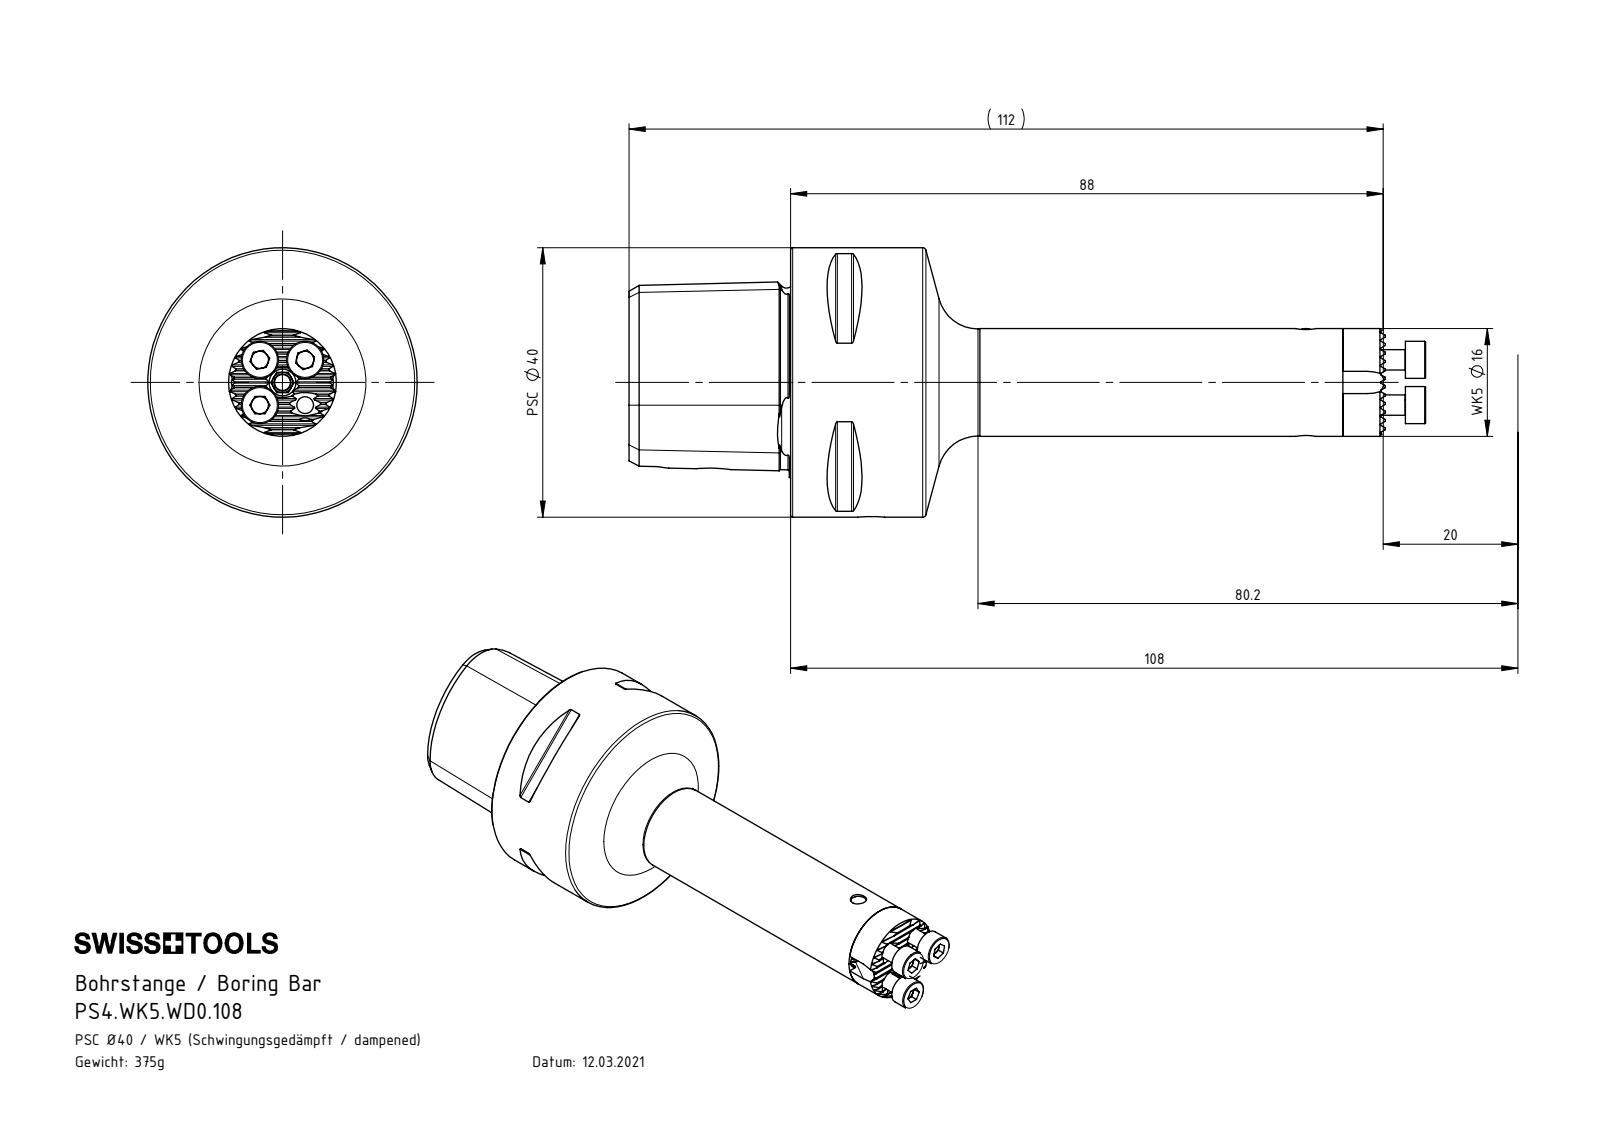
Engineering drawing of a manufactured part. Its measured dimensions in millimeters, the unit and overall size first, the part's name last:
Units: millimetres
Overall size (bounding box): 118.3 × 40 × 40
Round holes (diameter × count): ⌀2.5 ×7, ⌀2 ×3, ⌀3 ×2, ⌀4 ×2, ⌀3.3 ×1, ⌀4.5 ×1, ⌀4.6 ×1, ⌀5.4 ×1, ⌀6 ×1, ⌀10 ×1, ⌀12.5 ×1, ⌀13.2 ×1
Round bosses / shafts (diameter × count): ⌀3 ×5, ⌀5.5 ×3, ⌀40 ×1, ⌀16 ×1, ⌀13 ×1, ⌀12.6 ×1, ⌀12 ×1, ⌀10.8 ×1
Partial cylindrical surfaces — rounded edges, fillets, slot ends (radius × count): R0.12 ×13, R0.3 ×8, R1.65 ×4, R3 ×1
Main face-to-face distances: 4.5, 34.9, 24, 3, 15.52, 106, 82, 96, 72, 10
Hole centre spacings: 4.75, 6.72, 9.5, 7.5, 13.35, 15.9, 23.4, 23.5
Volume: 45 077 mm³ · Surface area: 21 111 mm²
Bodies: 18 solids, 485 faces (216 planar, 106 cylindrical, 163 other)
Part name (STEP PRODUCT): DIN 3771 - 5x2.5; DIN 3771 - 4x1; DIN 6325_ø3 x 5_2x6; WD0-ER1.005.022_A (+8 more)
STEP written by: SolidWorks 2017 (AUTOMOTIVE_DESIGN)
